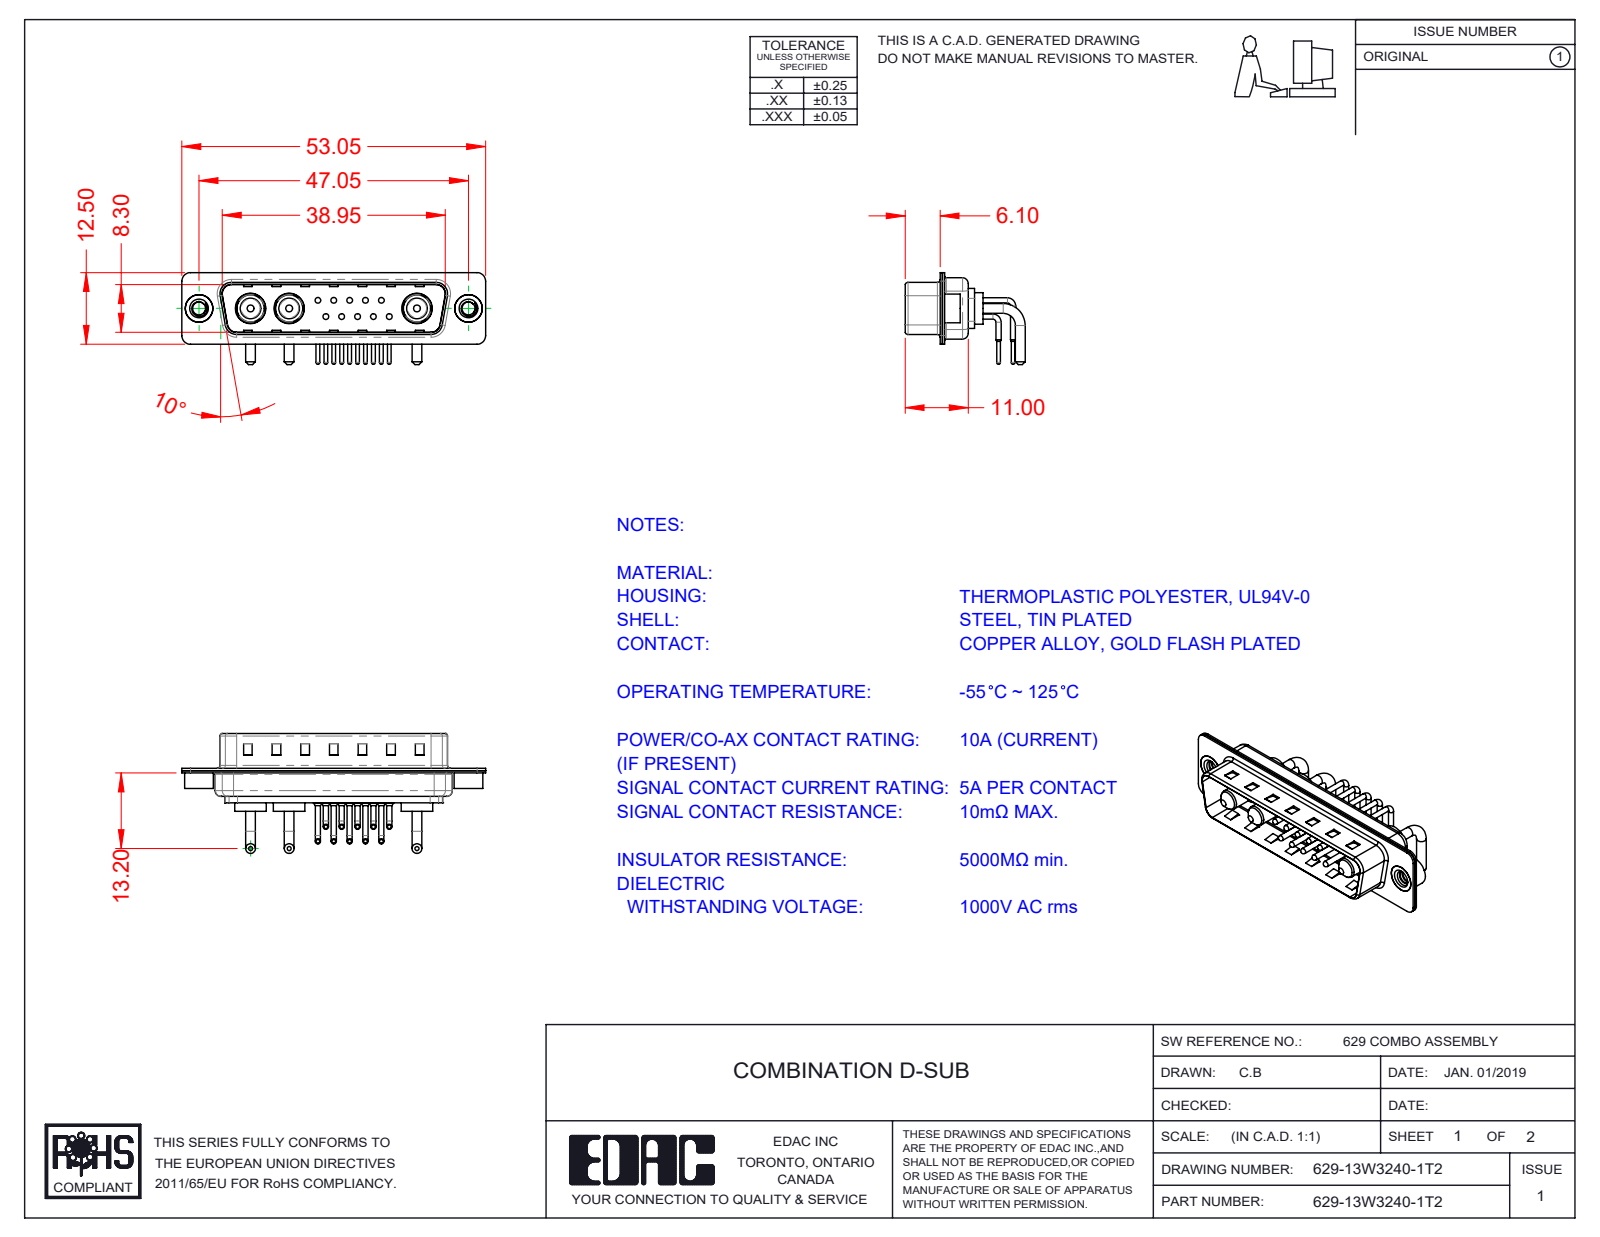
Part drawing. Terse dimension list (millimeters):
name: 629Combo Contact Row 1; 629Combo Shell Rear_25 Contacts; 629Combo Contact Row 2; 629Combo Shell Front_25 Contacts (+4 more)
written by: SolidWorks 2020 (CONFIG_CONTROL_DESIGN)
unit: mm
bodies: 21 solids, 1605 faces (841 planar, 560 cylindrical, 204 other)
size: 53.05 × 20.95 × 16.05
volume: 3 037 mm³; area: 7 218 mm²
holes: 10× ⌀0.75, 10× ⌀1.6, 10× ⌀2, 3× ⌀4.85, 3× ⌀5.3, 2× ⌀2.26, 2× ⌀4, 2× ⌀4.8
bosses: 20× ⌀0.9, 10× ⌀1.5, 10× ⌀1, 10× ⌀0.65, 6× ⌀1.7, 3× ⌀5.5, 3× ⌀5.2, 3× ⌀4.75
rounds: 16× R1.5, 12× R2, 10× R1.01, 8× R0.5, 8× R1.6, 4× R0.25, 4× R0.6, 4× R0.65
face distances: 0.4, 0.8, 9.5, 9.1, 8.7, 9.9, 5.6, 0.75, 1.2, 0.35
hole spacings: 3.16, 2.77, 5.04, 5.54, 7.49, 5.03, 8.31, 10.11
